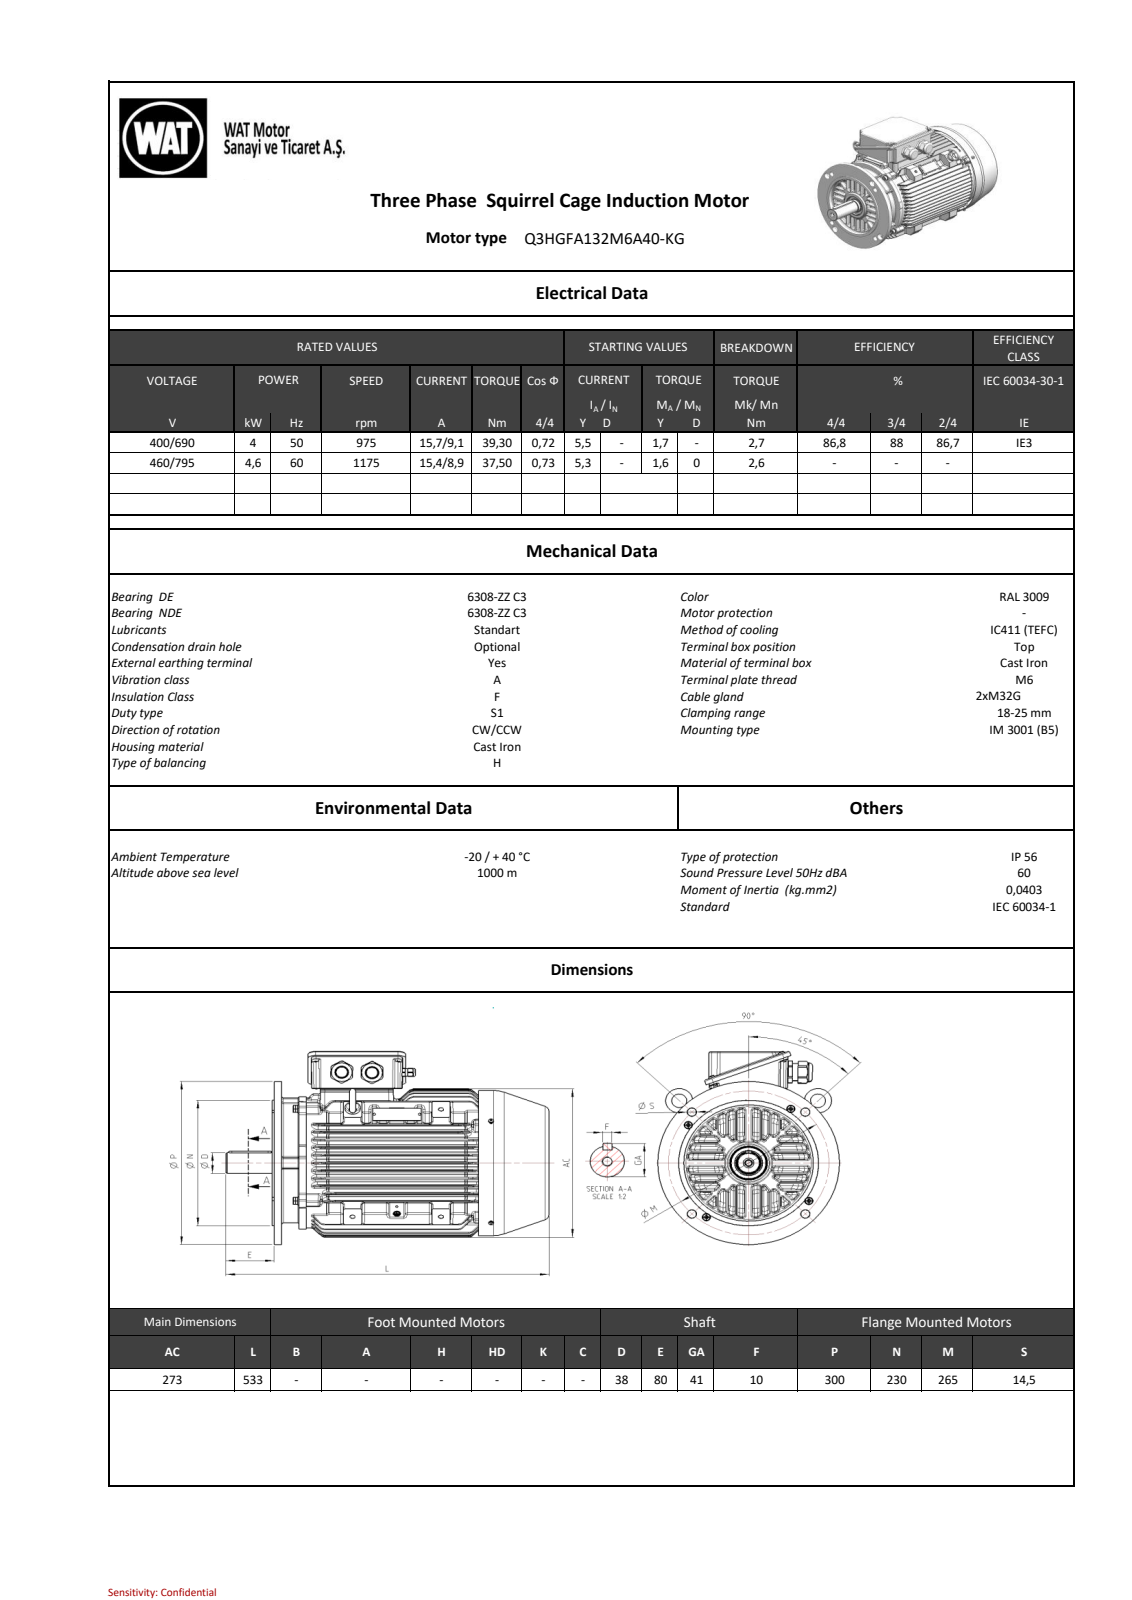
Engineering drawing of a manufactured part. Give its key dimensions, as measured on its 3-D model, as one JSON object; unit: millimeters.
{"part_name": "260021E4F5C7p82h", "step_written_by": "SIEMENS PLM Software NX 11.0 (AUTOMOTIVE_DESIGN)", "units": "millimeters", "bodies": {"solids": 0, "faces": 5186, "planar": 997, "cylindrical": 1415, "other": 2774}, "overall_size": [533, 355.41, 300], "round_holes": [[5.5, 8], [6.8, 8], [8.5, 6], [4.2, 4], [14, 4], [2.5, 2], [10, 2], [19, 2], [21, 2], [10.3, 1], [13, 1], [34.2, 1]], "round_bosses_or_shafts": [[13, 4], [8.65, 4], [8, 4], [36, 2], [34.5, 2], [31.25, 2], [25, 2], [12, 2]], "partial_cylinders_radius": [[4, 234], [3, 119], [1.5, 106], [2, 99], [1.8, 64], [28, 24], [35, 24], [44, 24]], "face_to_face_distances": [55.94, 13.76, 13.83, 27.59, 13.9, 27.73, 41.49, 55.44, 41.68, 27.85], "hole_center_spacings": [136, 73.55, 121.5, 171.83, 123.22, 183.52, 38.57, 42.2]}
